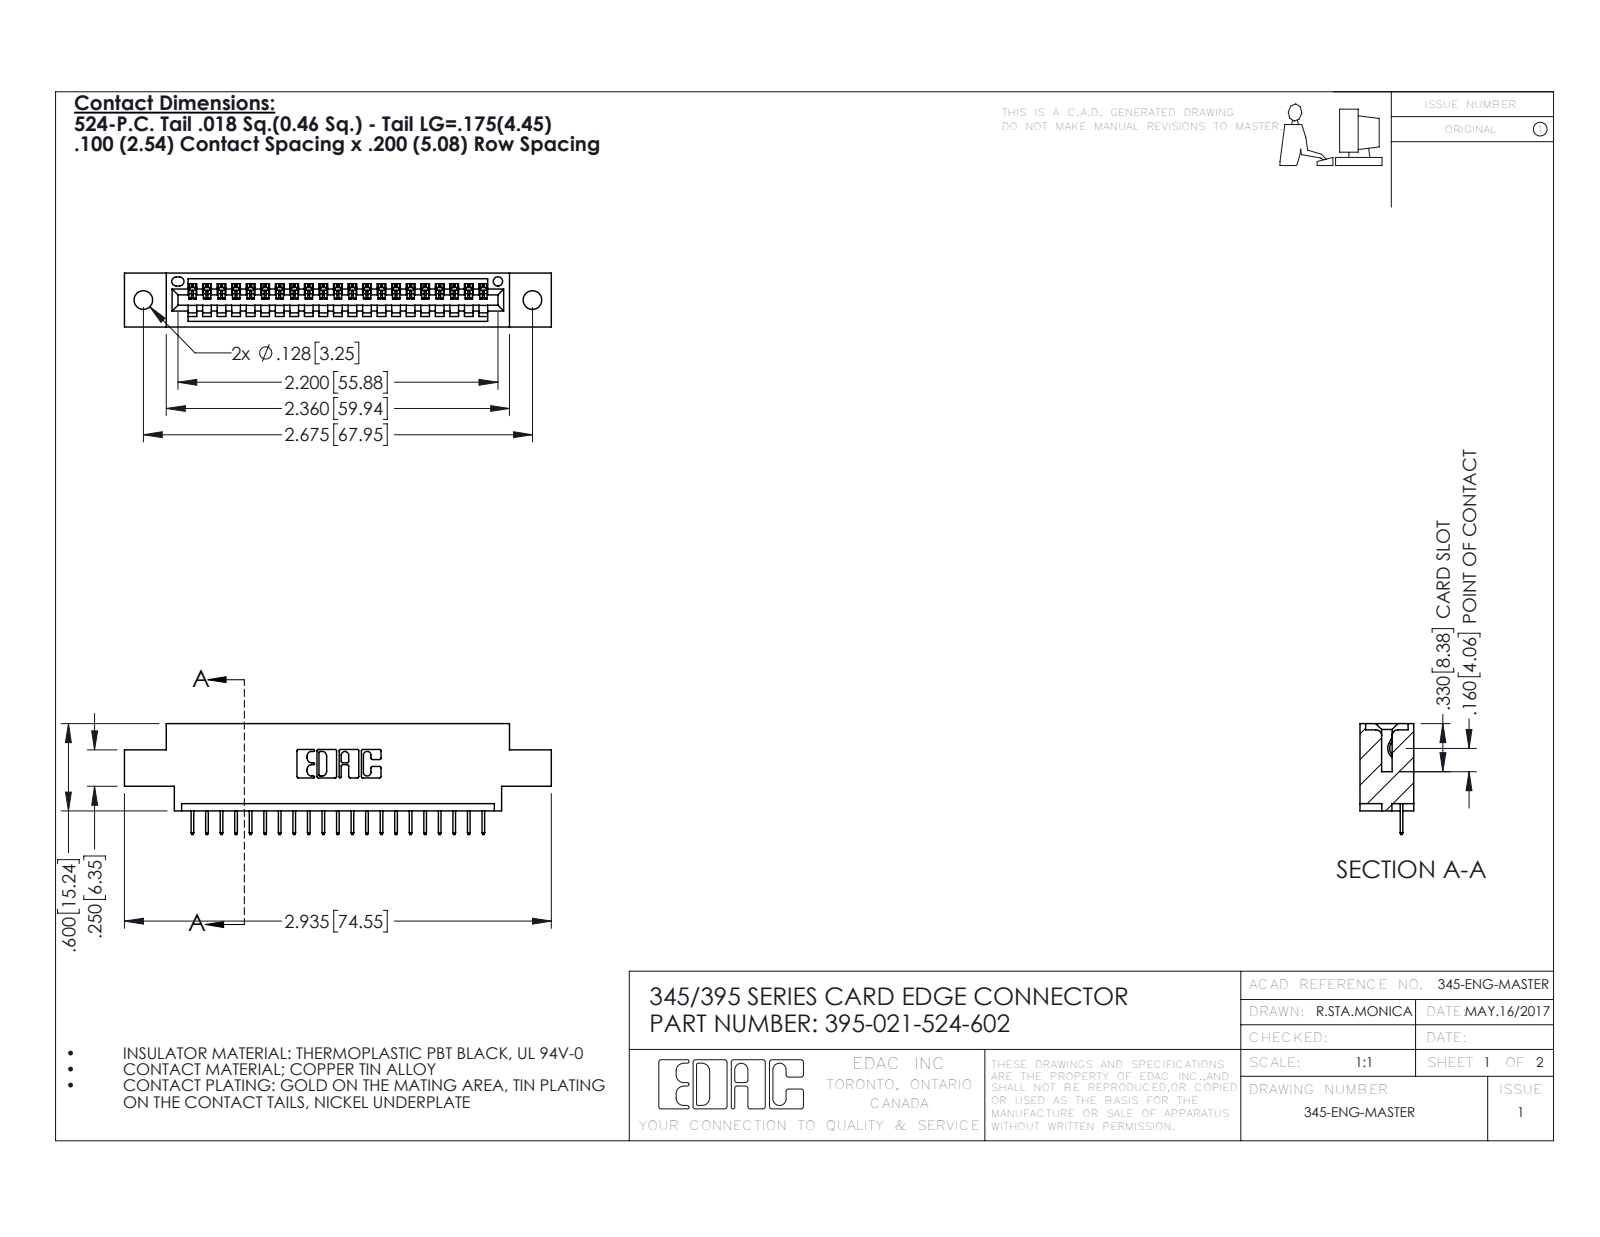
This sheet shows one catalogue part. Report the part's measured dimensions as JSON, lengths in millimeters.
{"part_name": "345-292-001_345-293-124; 395-021-524-602; 345 Part_0.170 Offset - 0.128 Dia", "step_written_by": "SolidWorks 2016 (CONFIG_CONTROL_DESIGN)", "units": "millimeters", "bodies": {"solids": 22, "faces": 1432, "planar": 1050, "cylindrical": 382, "other": 0}, "overall_size": [74.5, 19.4, 9.4], "volume_mm3": 6670, "surface_area_mm2": 8174, "round_holes": [[3.3, 2], [1.6, 1]], "partial_cylinders_radius": [[0.2, 42], [0.3, 22], [0.2, 6], [0.8, 6], [0.7, 3], [0.8, 2], [1, 2], [0.4, 1]], "face_to_face_distances": [9.4, 1.8, 7.6, 5.1, 2.5, 6.9, 0.6, 5.7, 1.8, 4.4], "hole_center_spacings": [6.9, 62, 67.9]}
